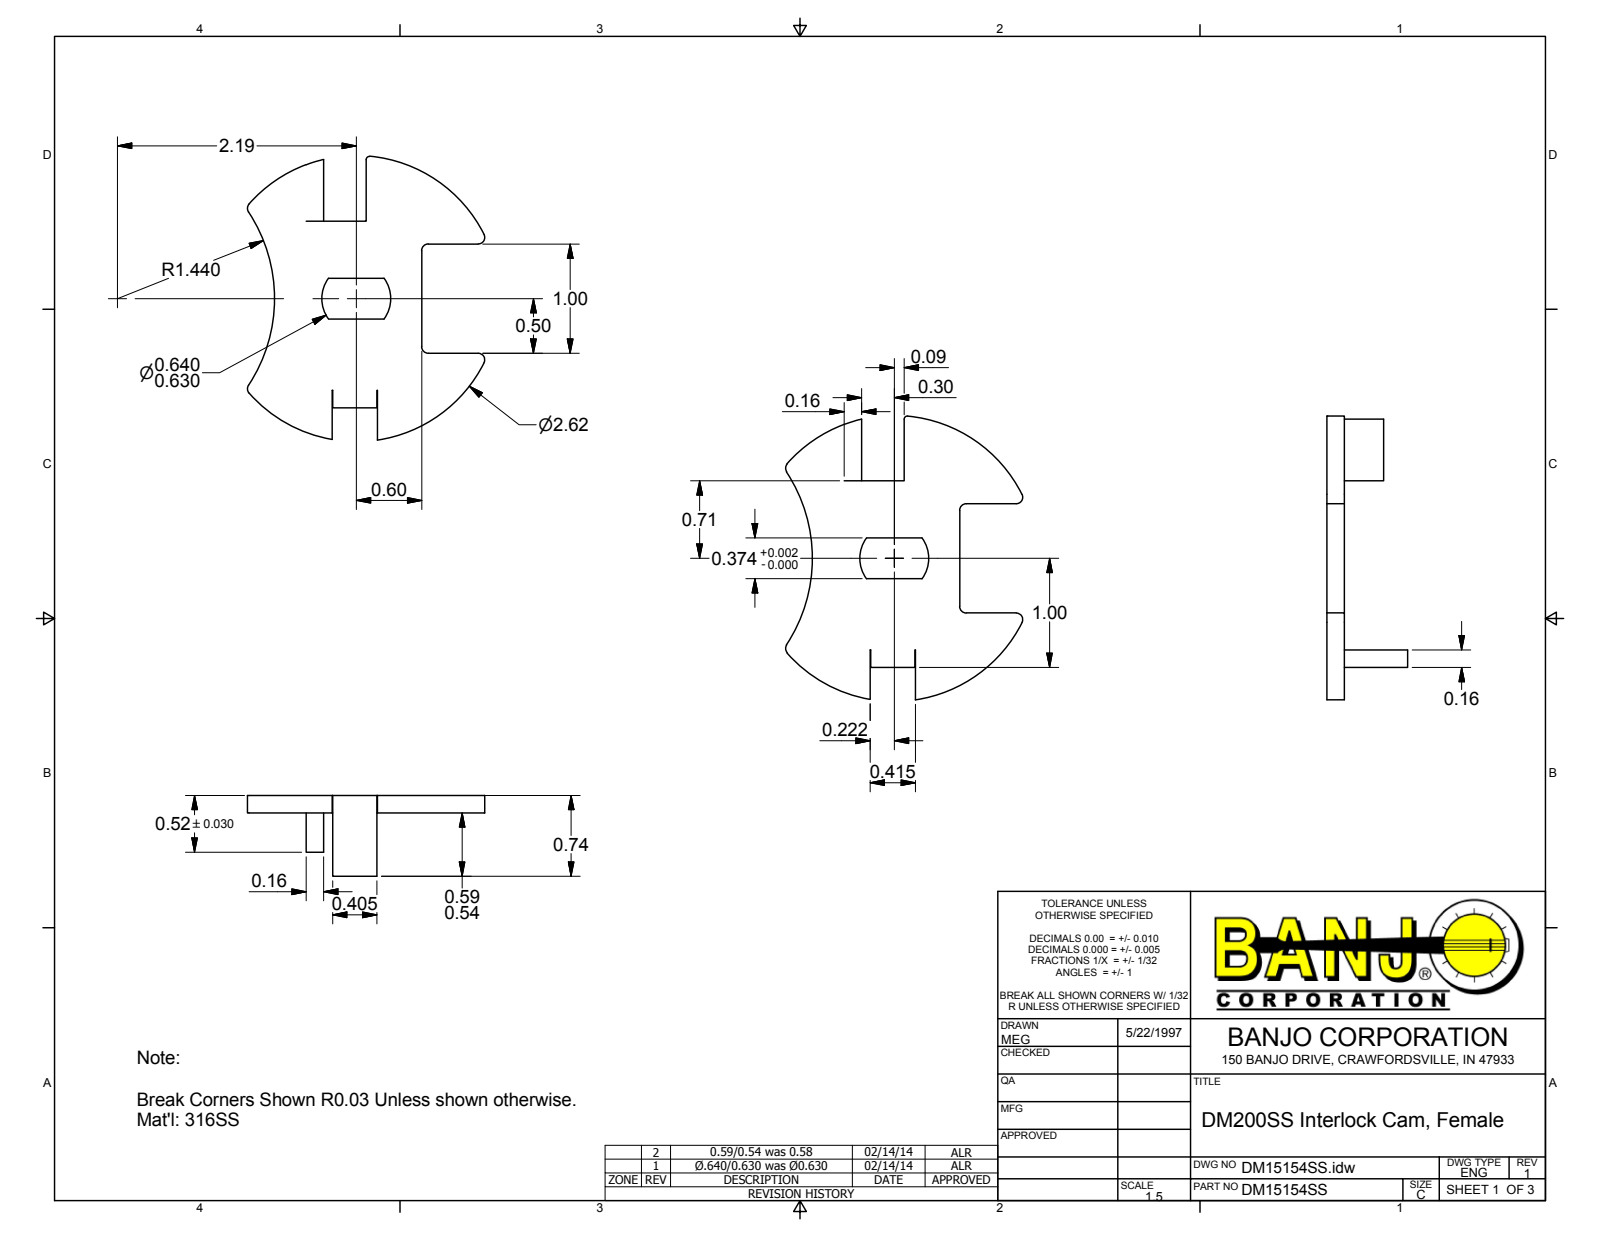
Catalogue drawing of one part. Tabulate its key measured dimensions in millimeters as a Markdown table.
| quantity | value |
| --- | --- |
| part name | DM15154SS |
| STEP written by | Autodesk Inventor 2016 (AUTOMOTIVE_DESIGN) |
| units | millimeters |
| bodies | 1 solid, 38 faces (22 planar, 16 cylindrical, 0 other) |
| overall size | 66.04 × 55.26 × 18.8 |
| volume | 10 211 mm³ |
| surface area | 6 592 mm² |
| partial cylindrical surfaces (radius × count) | 1.52 × 6, 4.06 × 2, 0.76 × 1, 8 × 1, 33.27 × 1, 36.58 × 1 |
| main face-to-face distances | 4.06, 7.95, 17.45, 22.86, 26.92, 39.37, 43.43, 20.75, 2.11, 6.17 |
